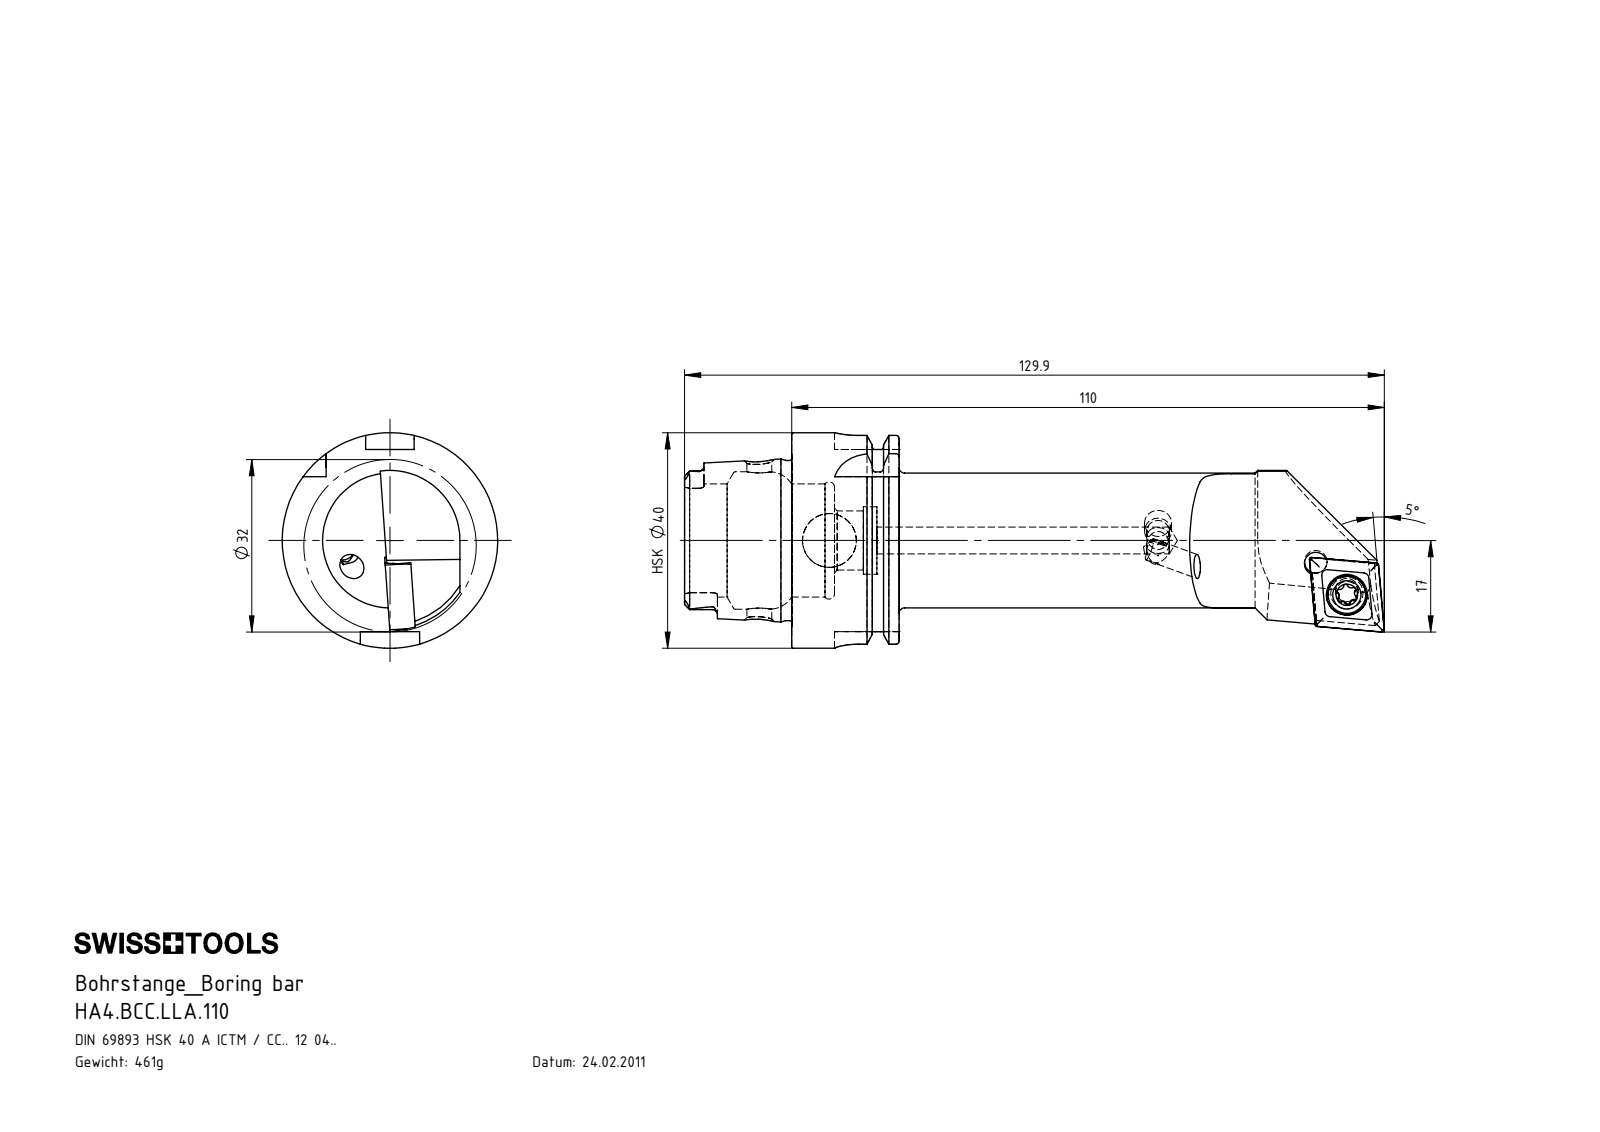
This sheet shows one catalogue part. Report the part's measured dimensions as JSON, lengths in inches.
{"part_name": "WCC-ER2.001.010_A; HA4.BCC.LLA.110; CCMT120404; HA4-BCC.LLA.110_A (+1 more)", "step_written_by": "SolidWorks 2017 (AUTOMOTIVE_DESIGN)", "units": "inches", "bodies": {"solids": 5, "faces": 308, "planar": 73, "cylindrical": 95, "other": 140}, "overall_size": [5.114, 1.575, 1.575], "volume_in3": 3.641, "surface_area_in2": 28.36, "round_holes": [[0.165, 4], [0.197, 2], [0.157, 1], [0.181, 1], [0.217, 1], [0.299, 1], [0.394, 1], [0.433, 1], [0.492, 1], [0.827, 1], [1.004, 1]], "round_bosses_or_shafts": [[0.197, 2], [1.575, 1], [1.368, 1], [1.17, 1], [0.984, 1], [0.276, 1]], "partial_cylinders_radius": [[0.015, 6], [0.035, 6], [0.027, 3], [0.027, 3], [0.177, 3], [0.072, 2], [0.074, 2], [0.118, 1]], "face_to_face_distances": [0.785, 0.176, 0.313, 0.472, 0.783, 1.096, 1.569, 1.406, 0.622, 0.309], "hole_center_spacings": [0.316, 0.322]}
